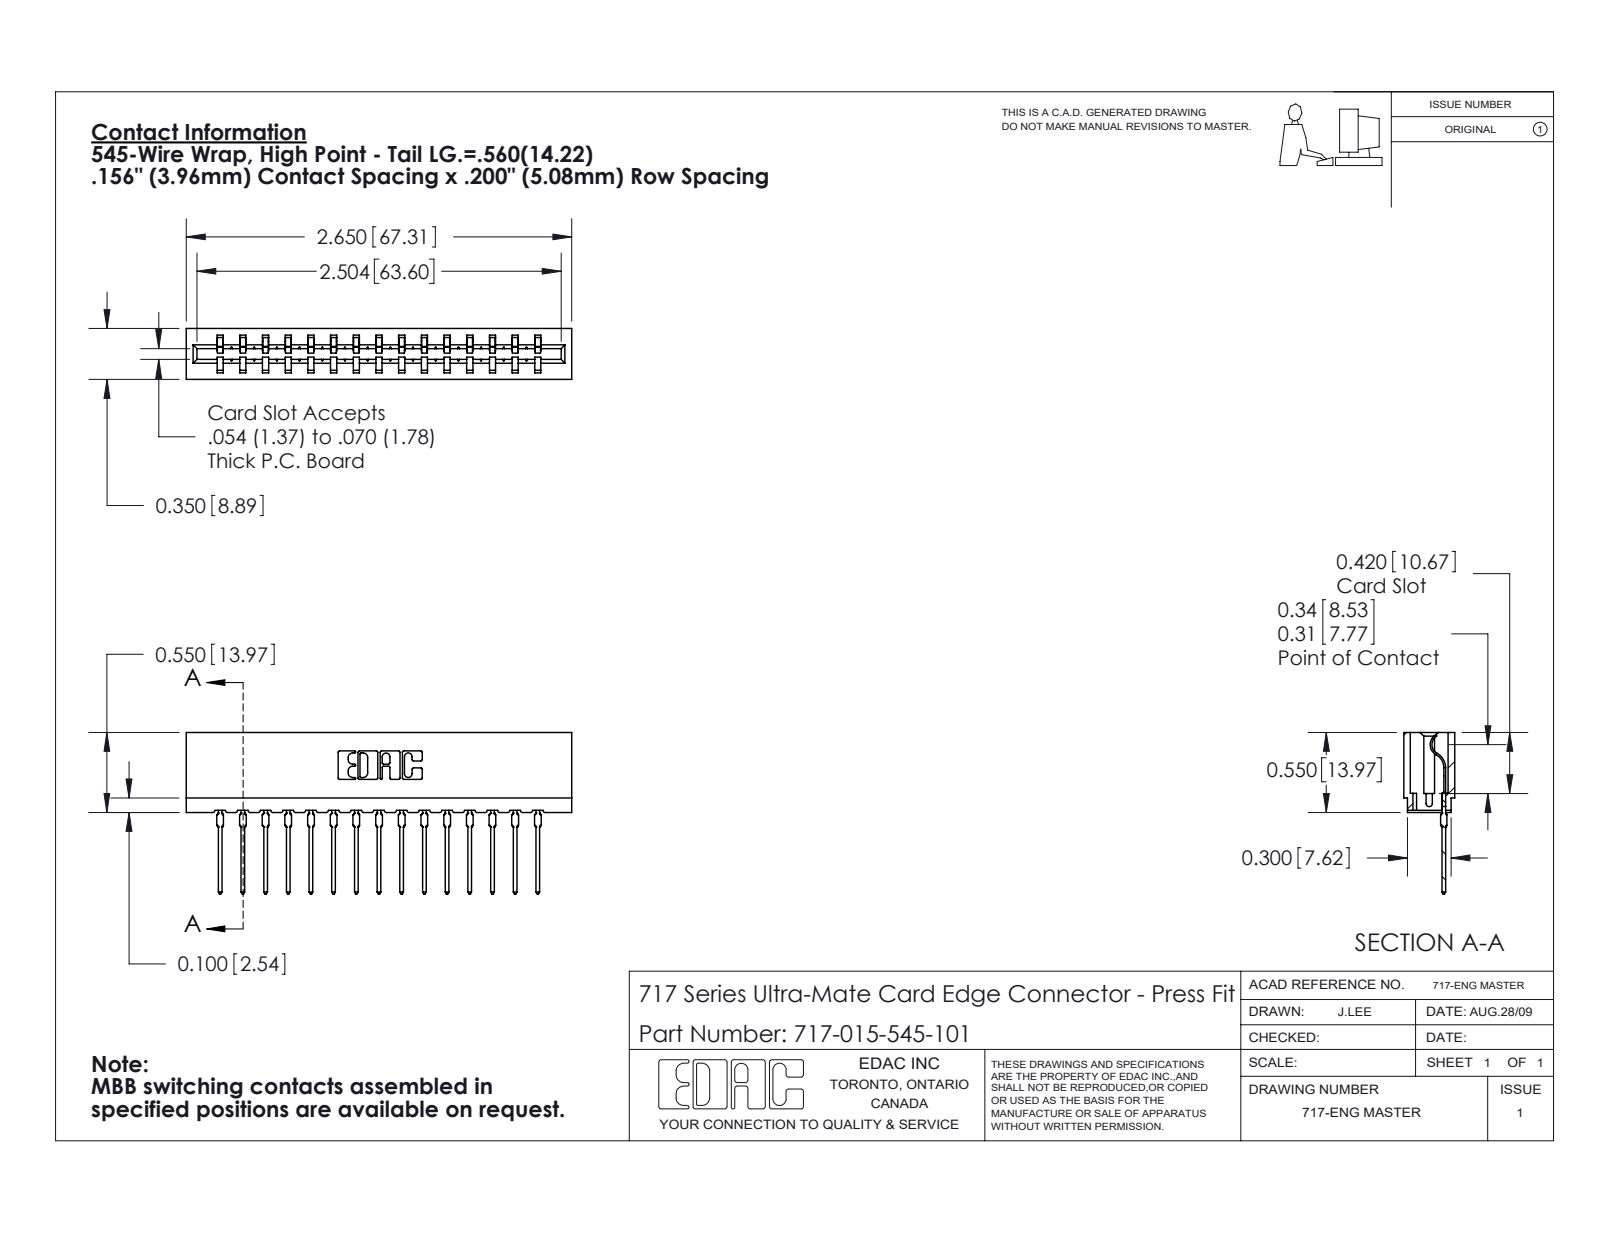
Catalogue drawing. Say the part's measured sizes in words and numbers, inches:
The part is named "717-015-545-101; 745-292-001_545; 717 Part_Insulator Option - 06". Its 3-D file was written by "SolidWorks 2020 (CONFIG_CONTROL_DESIGN)". It is 16 solids with 1789 faces: 1074 planar, 325 cylindrical and 390 other. Overall it measures 2.65 by 1.109 by 0.35 inches. Its volume is 0.357 cubic inches and its surface area 12.64 square inches. Partial cylindrical surfaces (rounded edges, fillets, slot ends): 30 of radius 0.015, 30 of radius 0.021, 22 of radius 0.01, 6 of radius 0.007, 6 of radius 0.031, 4 of radius 0.005, 4 of radius 0.011, 3 of radius 0.026. The main face-to-face distances are 0.212, 0.138, 0.35, 0.156, 0.624, 0.468, 0.312, 0.074, 0.198, 0.063.
